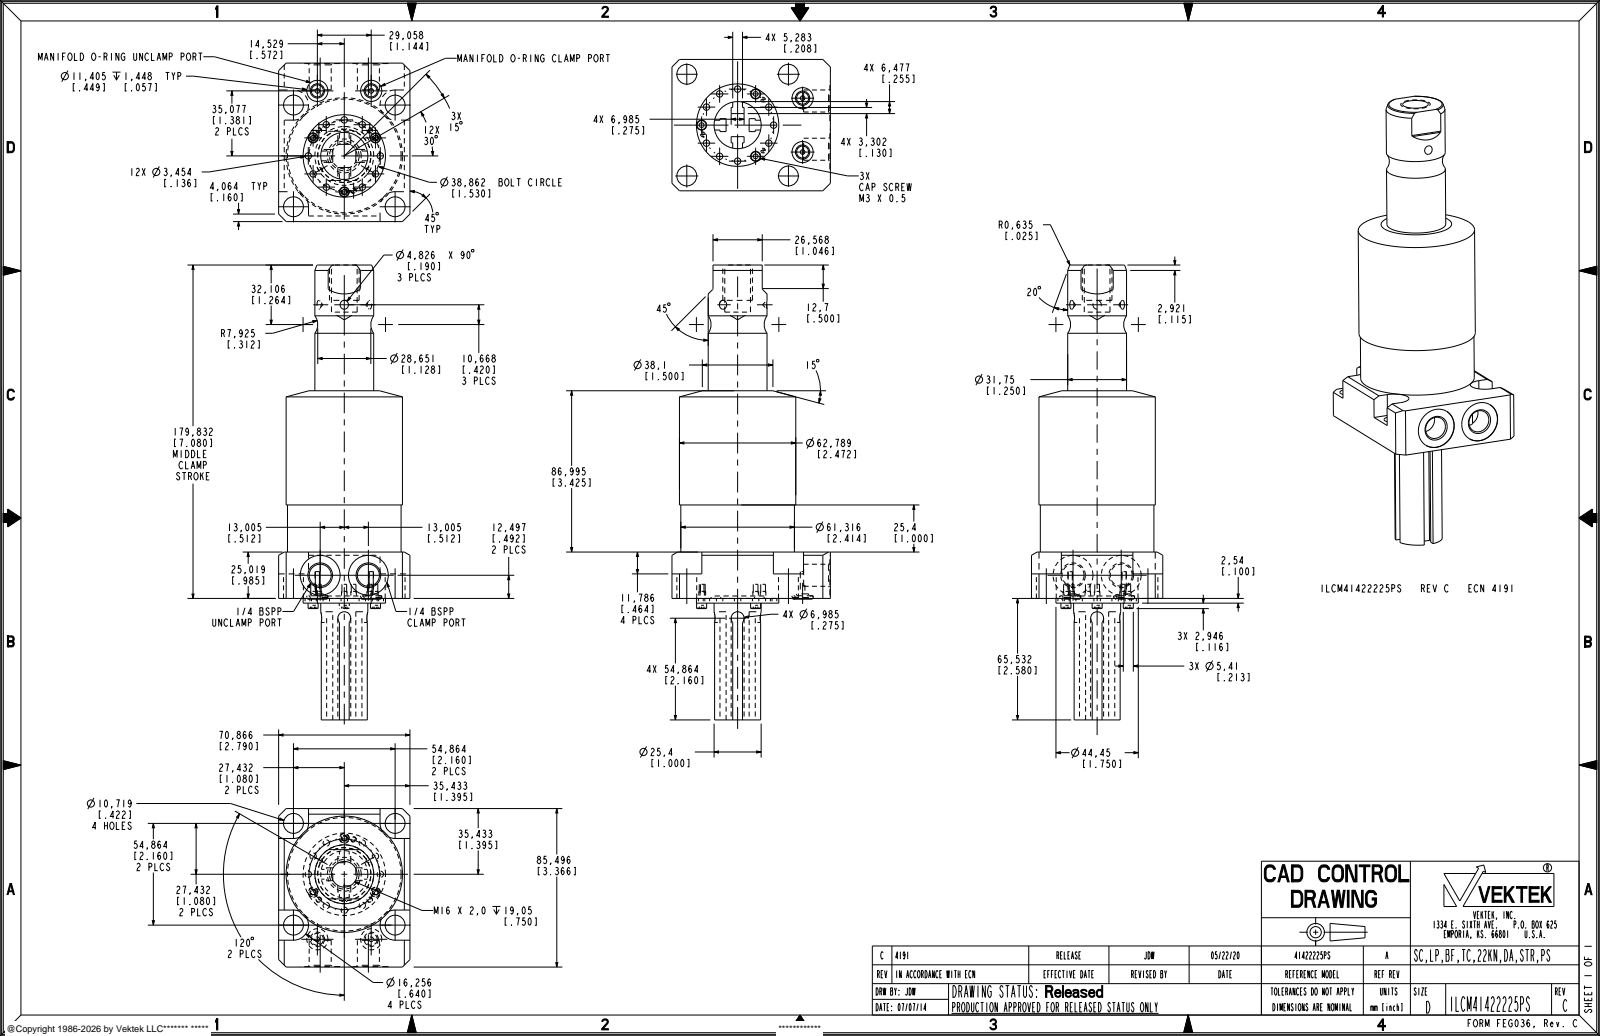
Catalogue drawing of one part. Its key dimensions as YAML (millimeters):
part_name: "ILCM41422225PS"
step_written_by: "PRO/ENGINEER BY PARAMETRIC TECHNOLOGY CORPORATION, 2013320 (AUTOMOTIVE_DESIGN)"
units: millimeters
bodies: {solids: 1, faces: 282, planar: 134, cylindrical: 114, other: 34}
overall_size: [245.36, 85.5, 70.87]
volume: 466620
surface_area: 59365
round_holes:
  - {diameter: 3.45, count: 12}
  - {diameter: 2.54, count: 6}
  - {diameter: 10.72, count: 4}
  - {diameter: 2.49, count: 2}
  - {diameter: 6.5, count: 2}
  - {diameter: 11.4, count: 2}
  - {diameter: 11.89, count: 2}
  - {diameter: 21.49, count: 2}
  - {diameter: 13.87, count: 1}
  - {diameter: 28.7, count: 1}
round_bosses_or_shafts:
  - {diameter: 3, count: 6}
  - {diameter: 5.41, count: 3}
  - {diameter: 62.79, count: 1}
  - {diameter: 61.32, count: 1}
  - {diameter: 44.45, count: 1}
  - {diameter: 31.75, count: 1}
  - {diameter: 25.4, count: 1}
  - {diameter: 18.26, count: 1}
partial_cylinders:
  - {radius: 8.13, count: 4}
  - {radius: 0.76, count: 2}
  - {radius: 3.49, count: 2}
face_to_face_distances: [25.02, 70.86, 2.73, 9.71, 3.58, 8.86, 0.85, 6.13, 41.65, 29.21]
hole_center_spacings: [19.43, 33.66, 10.06, 19.44, 37.54, 20.64, 27.49, 28.57]
